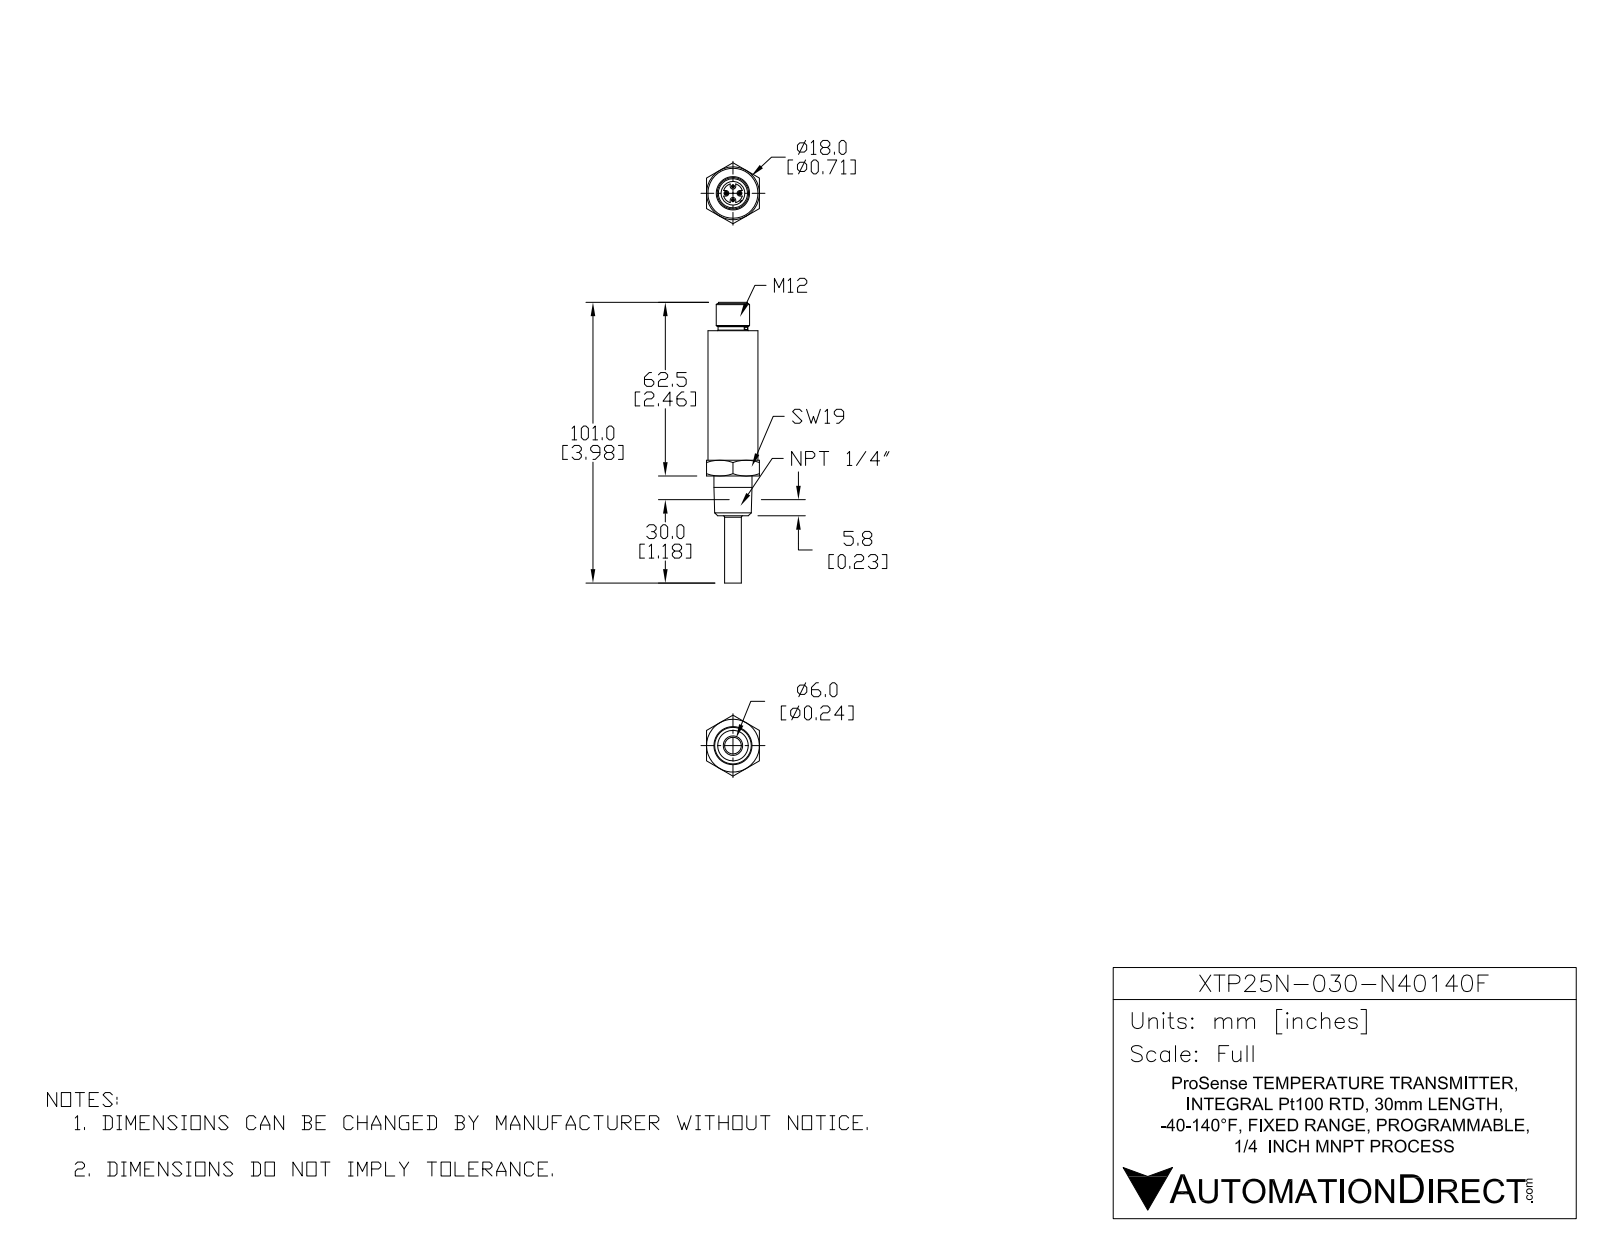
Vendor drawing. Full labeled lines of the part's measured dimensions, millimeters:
Part name (STEP PRODUCT): XTP25N-030-N40140F
STEP written by: SolidWorks 2015 (AUTOMOTIVE_DESIGN)
Units: millimetres
Bodies: 1 solid, 117 faces (43 planar, 34 cylindrical, 40 other)
Overall size (bounding box): 101 × 21.94 × 19
Volume: 16 667 mm³ · Surface area: 5 627 mm²
Round holes (diameter × count): ⌀4 ×1, ⌀8.5 ×1
Round bosses / shafts (diameter × count): ⌀1.02 ×4, ⌀18 ×1, ⌀13.72 ×1, ⌀12 ×1, ⌀10.7 ×1, ⌀10.5 ×1, ⌀6 ×1
Partial cylindrical surfaces — rounded edges, fillets, slot ends (radius × count): R1 ×4, R3.5 ×1, R4.25 ×1
Main face-to-face distances: 19, 52.3, 14.3, 66.6, 20, 5.7, 46.6, 76.8, 62.5, 56.8
